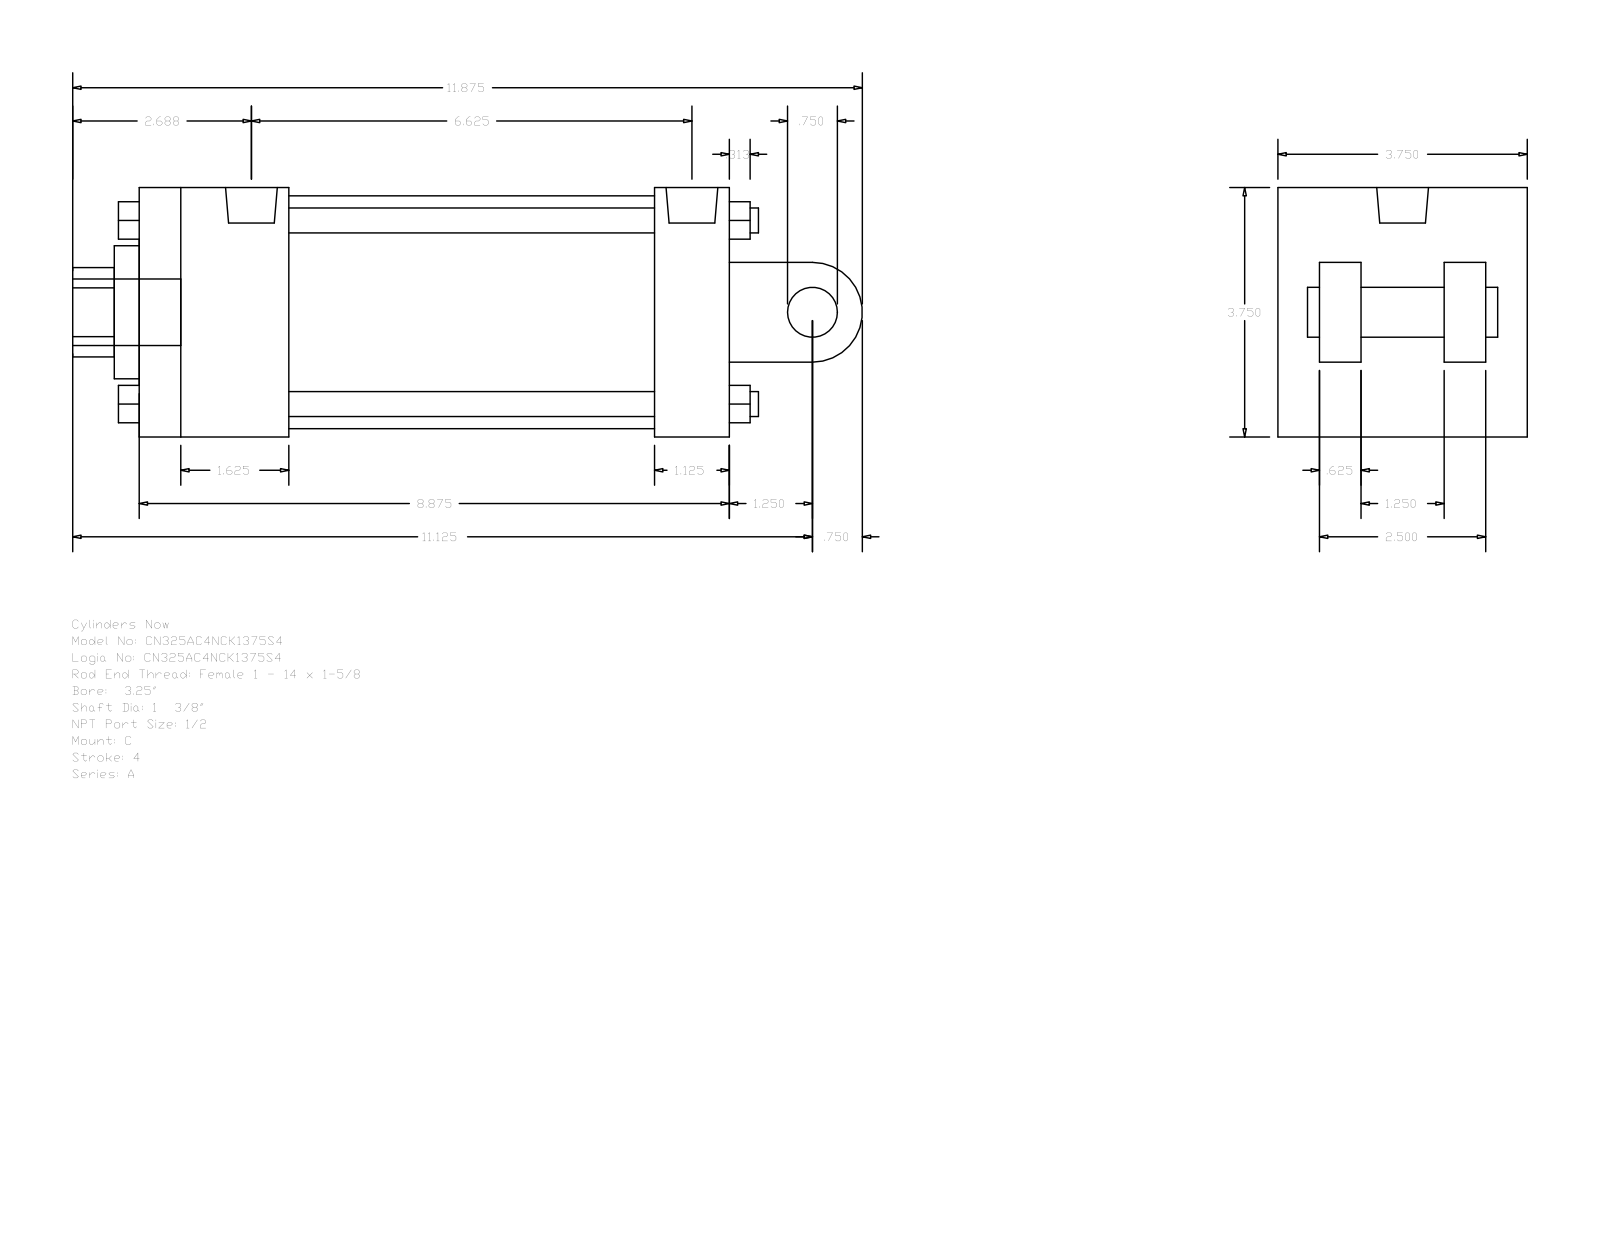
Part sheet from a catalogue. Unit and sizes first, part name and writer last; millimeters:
Units: millimetres
Overall size (bounding box): 301.62 × 95.25 × 95.25
Round holes (diameter × count): ⌀8.73 ×2, ⌀19.77 ×1, ⌀34.92 ×1, ⌀50.8 ×1, ⌀88.9 ×1
Round bosses / shafts (diameter × count): ⌀9.53 ×4, ⌀8.73 ×2, ⌀25.4 ×1, ⌀19.77 ×1, ⌀19.05 ×1
Partial cylindrical surfaces — rounded edges, fillets, slot ends (radius × count): R17.06 ×1, R19.05 ×1
Main face-to-face distances: 95.24, 15.87, 225.42, 28.57, 63.5, 66.67, 79.37, 31.74, 47.63, 196.85
Hole centre spacings: 3.18
Bodies: 0 solids, 135 faces (102 planar, 33 cylindrical, 0 other)
Part name (STEP PRODUCT): A_C__0325_1.375
STEP written by: GSSL Pune (CONFIG_CONTROL_DESIGN)
